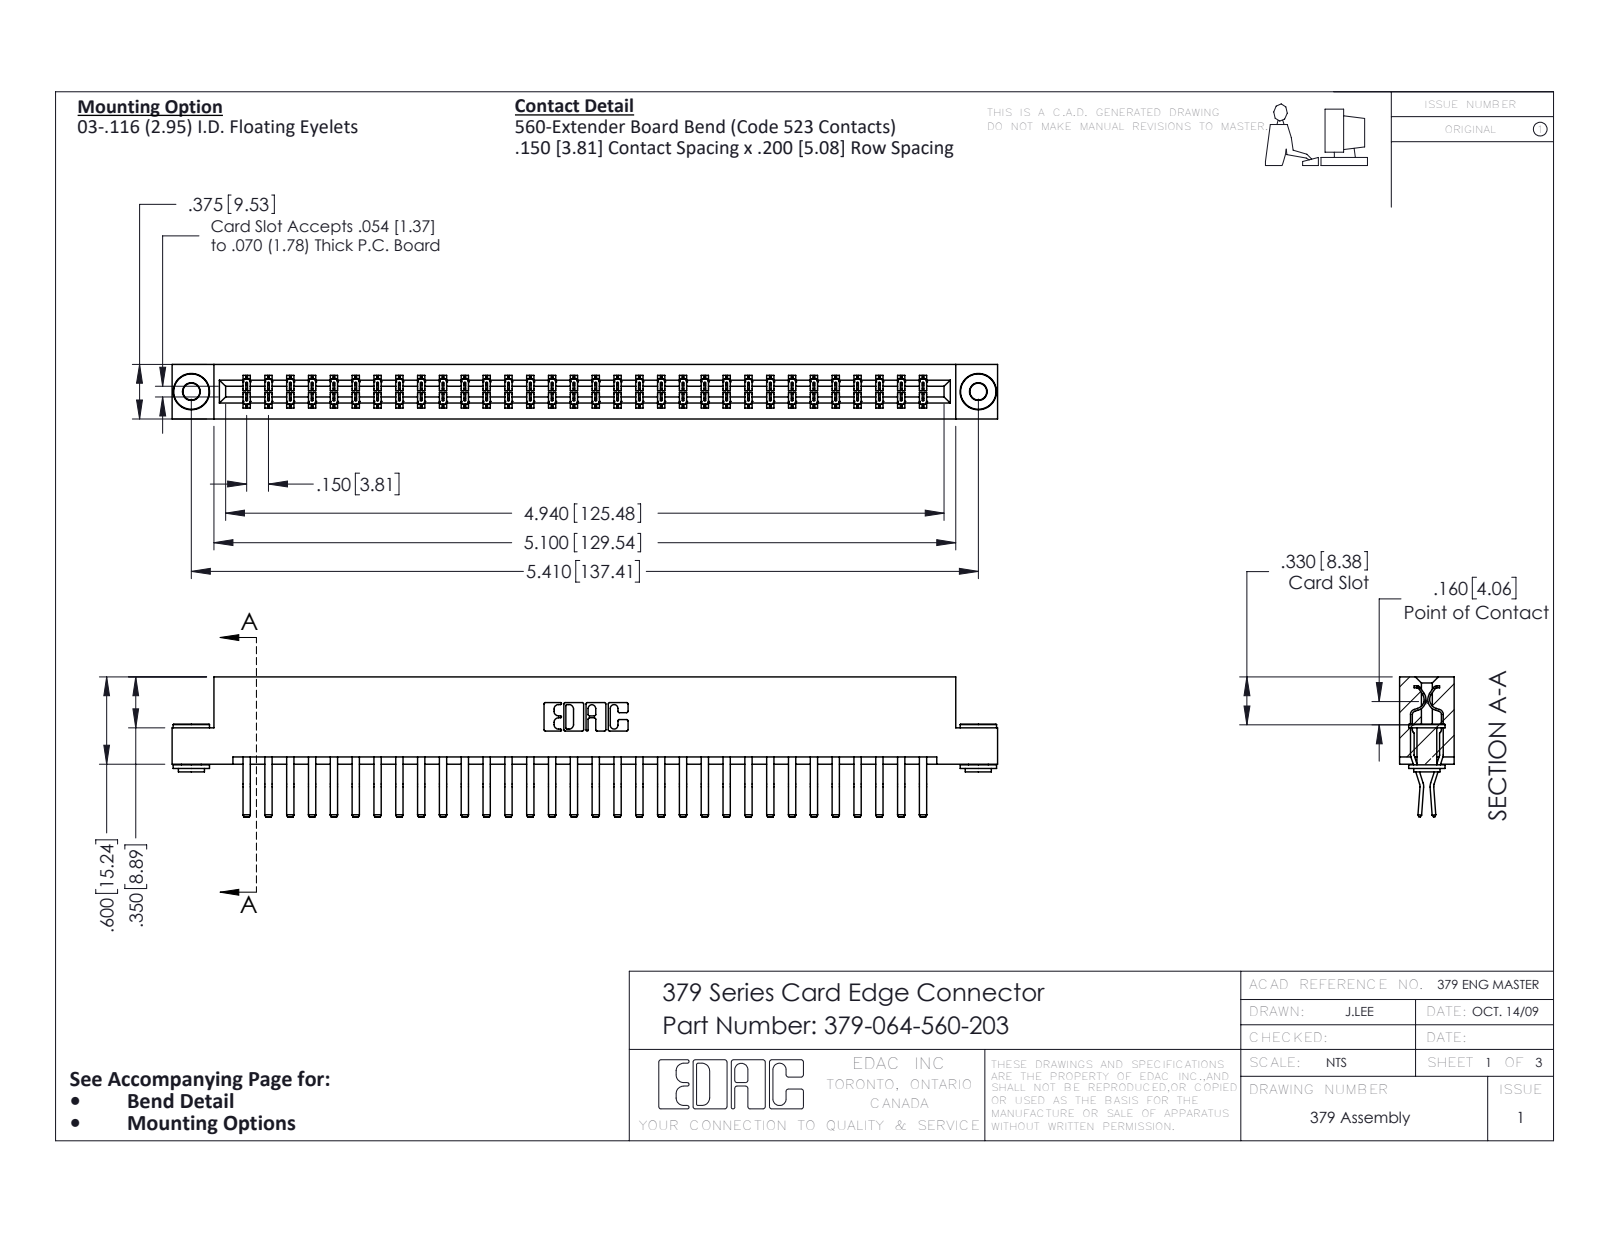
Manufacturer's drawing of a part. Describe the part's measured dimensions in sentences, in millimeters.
The part is named "379-064-560-203; 379 Part_Flush - .156 Dia - TH; 345-250-002_345-250-002-102; 345-292-001_560 Tail". Its 3-D file was written by "SolidWorks 2016 (CONFIG_CONTROL_DESIGN)". It is 67 solids with 3608 faces: 2384 planar, 1216 cylindrical and 8 other. Overall it measures 144.1 by 24.4 by 9.5 millimeters. Its volume is 15 700 cubic millimeters and its surface area 18 950 square millimeters. Round holes: 2 of diameter 2.9, 2 of diameter 4. Round bosses or shafts: 2 of diameter 6.4, 2 of diameter 4.6, 2 of diameter 3.5. Partial cylindrical surfaces (rounded edges, fillets, slot ends): 96 of radius 0.2, 22 of radius 0.3, 6 of radius 0.2, 6 of radius 0.8, 3 of radius 0.7, 2 of radius 0.3, 2 of radius 0.4, 2 of radius 0.6. The main face-to-face distances are 7.6, 1.9, 9.5, 15.2, 0.6, 5.7, 3.8, 11.4, 5.1, 3.8. The hole center spacings are 137.4.
